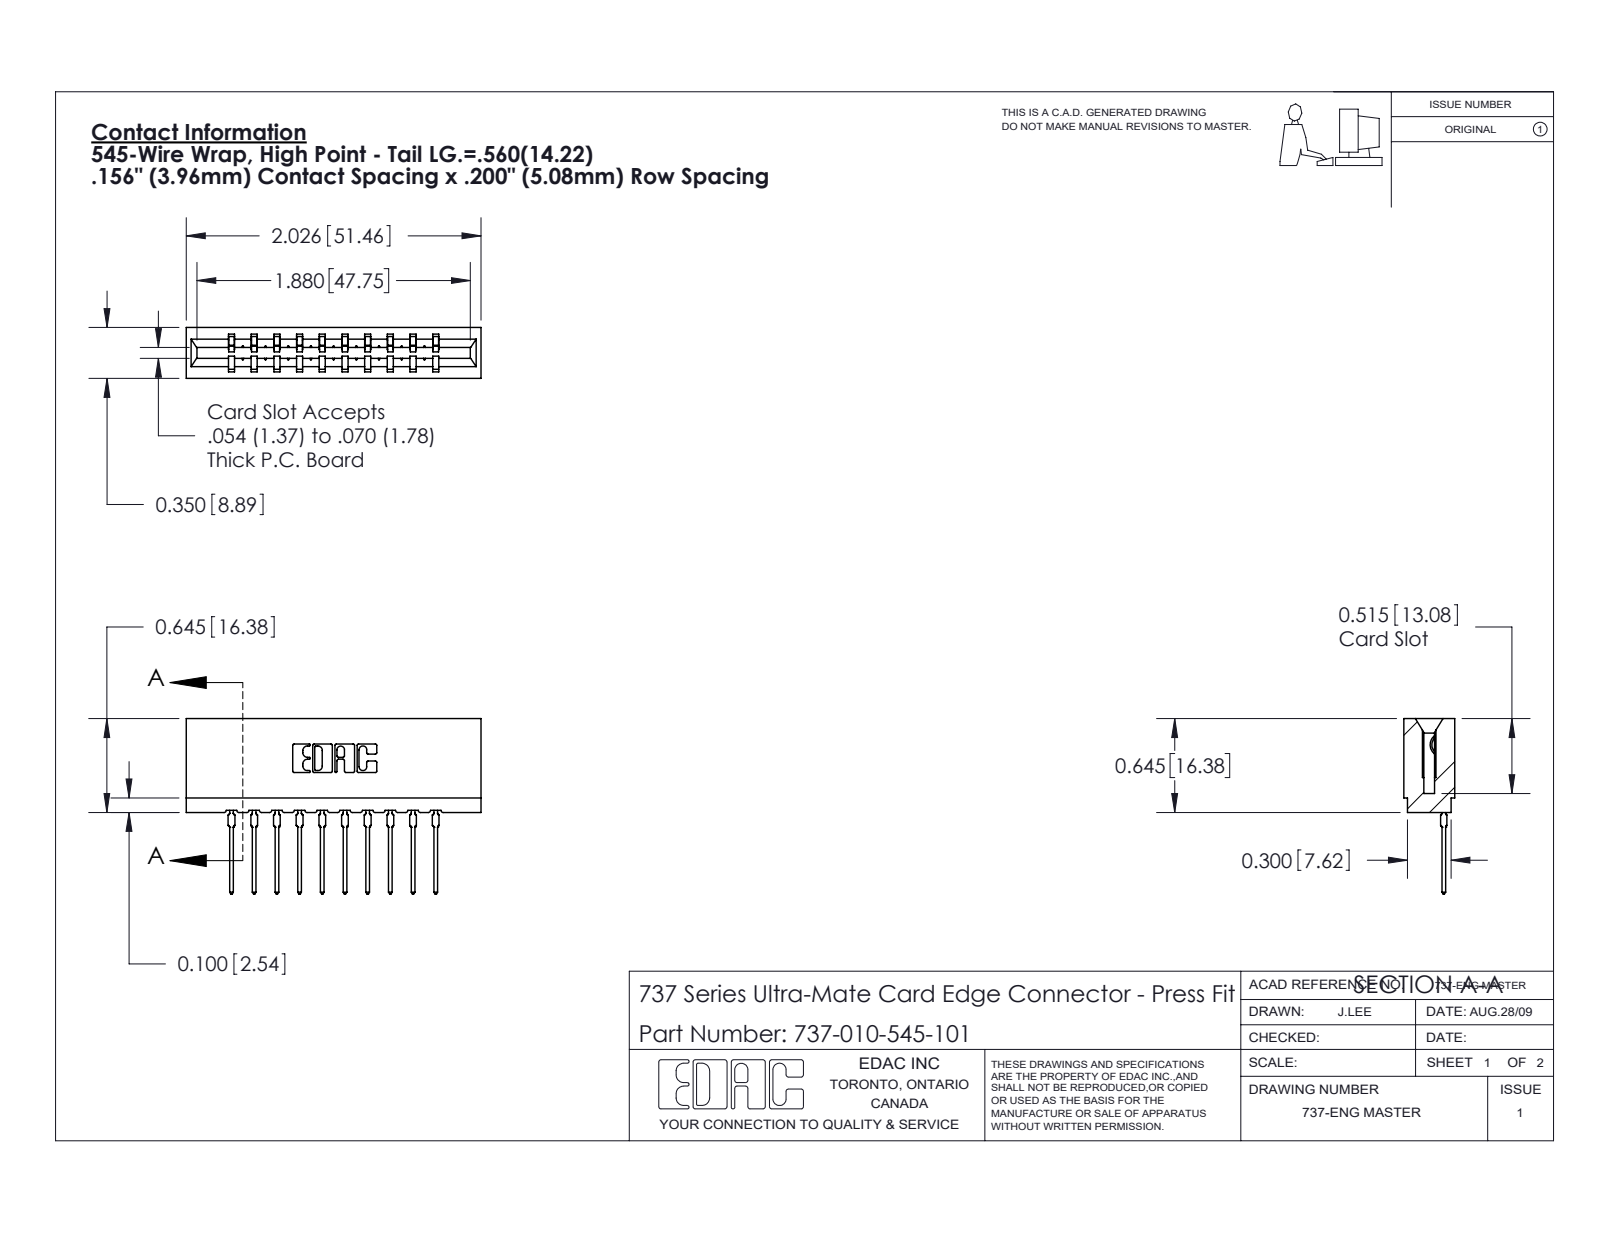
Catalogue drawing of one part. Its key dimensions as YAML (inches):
part_name: "745-292-001_545; 737-010-545-101; 737 Part_Insulator Option - 01"
step_written_by: "SolidWorks 2020 (CONFIG_CONTROL_DESIGN)"
units: inches
bodies: {solids: 11, faces: 1224, planar: 734, cylindrical: 230, other: 260}
overall_size: [2.026, 1.206, 0.35]
volume: 0.319
surface_area: 10.22
partial_cylinders:
  - {radius: 0.01, count: 22}
  - {radius: 0.015, count: 20}
  - {radius: 0.021, count: 20}
  - {radius: 0.007, count: 6}
  - {radius: 0.031, count: 6}
  - {radius: 0.005, count: 4}
  - {radius: 0.011, count: 4}
  - {radius: 0.026, count: 3}
face_to_face_distances: [0.156, 0.138, 0.212, 0.35, 0.624, 0.312, 0.354, 0.78, 0.468, 0.198]
